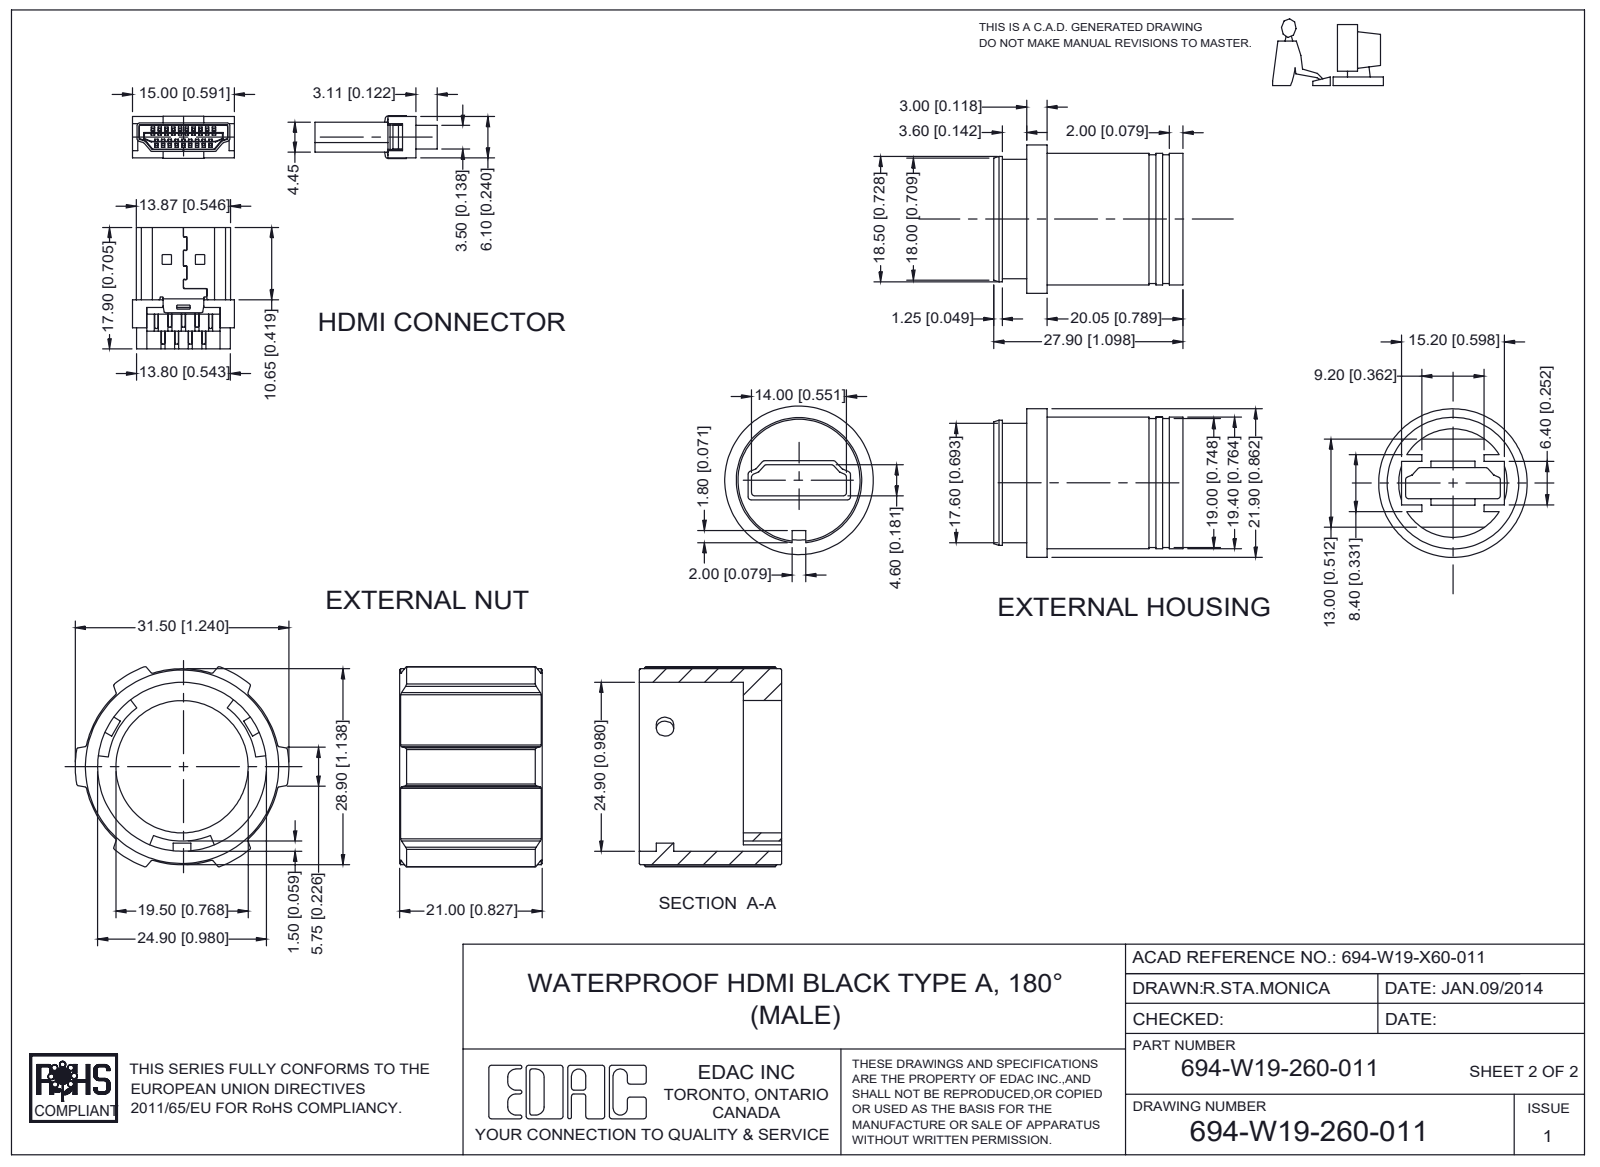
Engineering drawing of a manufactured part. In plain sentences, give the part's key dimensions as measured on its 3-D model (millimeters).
The part is named "HDMI SHELL 694-W19-X60-011; HDMI HOUSING1 694-W19-X60-011; HDMI CONTACT3 694-W19-X60-011; HOUSING OUTER 694-W19-X60-011 (+7 more)". Its 3-D file was written by "SolidWorks 2020 (AUTOMOTIVE_DESIGN)". It is 25 solids with 2367 faces: 1591 planar, 761 cylindrical and 15 other. Overall it measures 35.4 by 31.5 by 29.5 millimeters. Its volume is 9 886 cubic millimeters and its surface area 12 696 square millimeters. Round holes: 1 of diameter 15.94, 1 of diameter 17.1, 1 of diameter 19.5, 1 of diameter 24.9. Round bosses or shafts: 1 of diameter 21.84, 1 of diameter 21.5, 1 of diameter 19.34, 1 of diameter 18.94, 1 of diameter 18.44, 1 of diameter 17.54. Partial cylindrical surfaces (rounded edges, fillets, slot ends): 284 of radius 0.15, 114 of radius 0.11, 29 of radius 0.3, 26 of radius 0.5, 19 of radius 0.15, 18 of radius 0.2, 10 of radius 0.1, 10 of radius 0.17. The main face-to-face distances are 0.4, 1, 3, 1.65, 8.65, 2.38, 5.65, 9.15, 7.4, 13.5.
